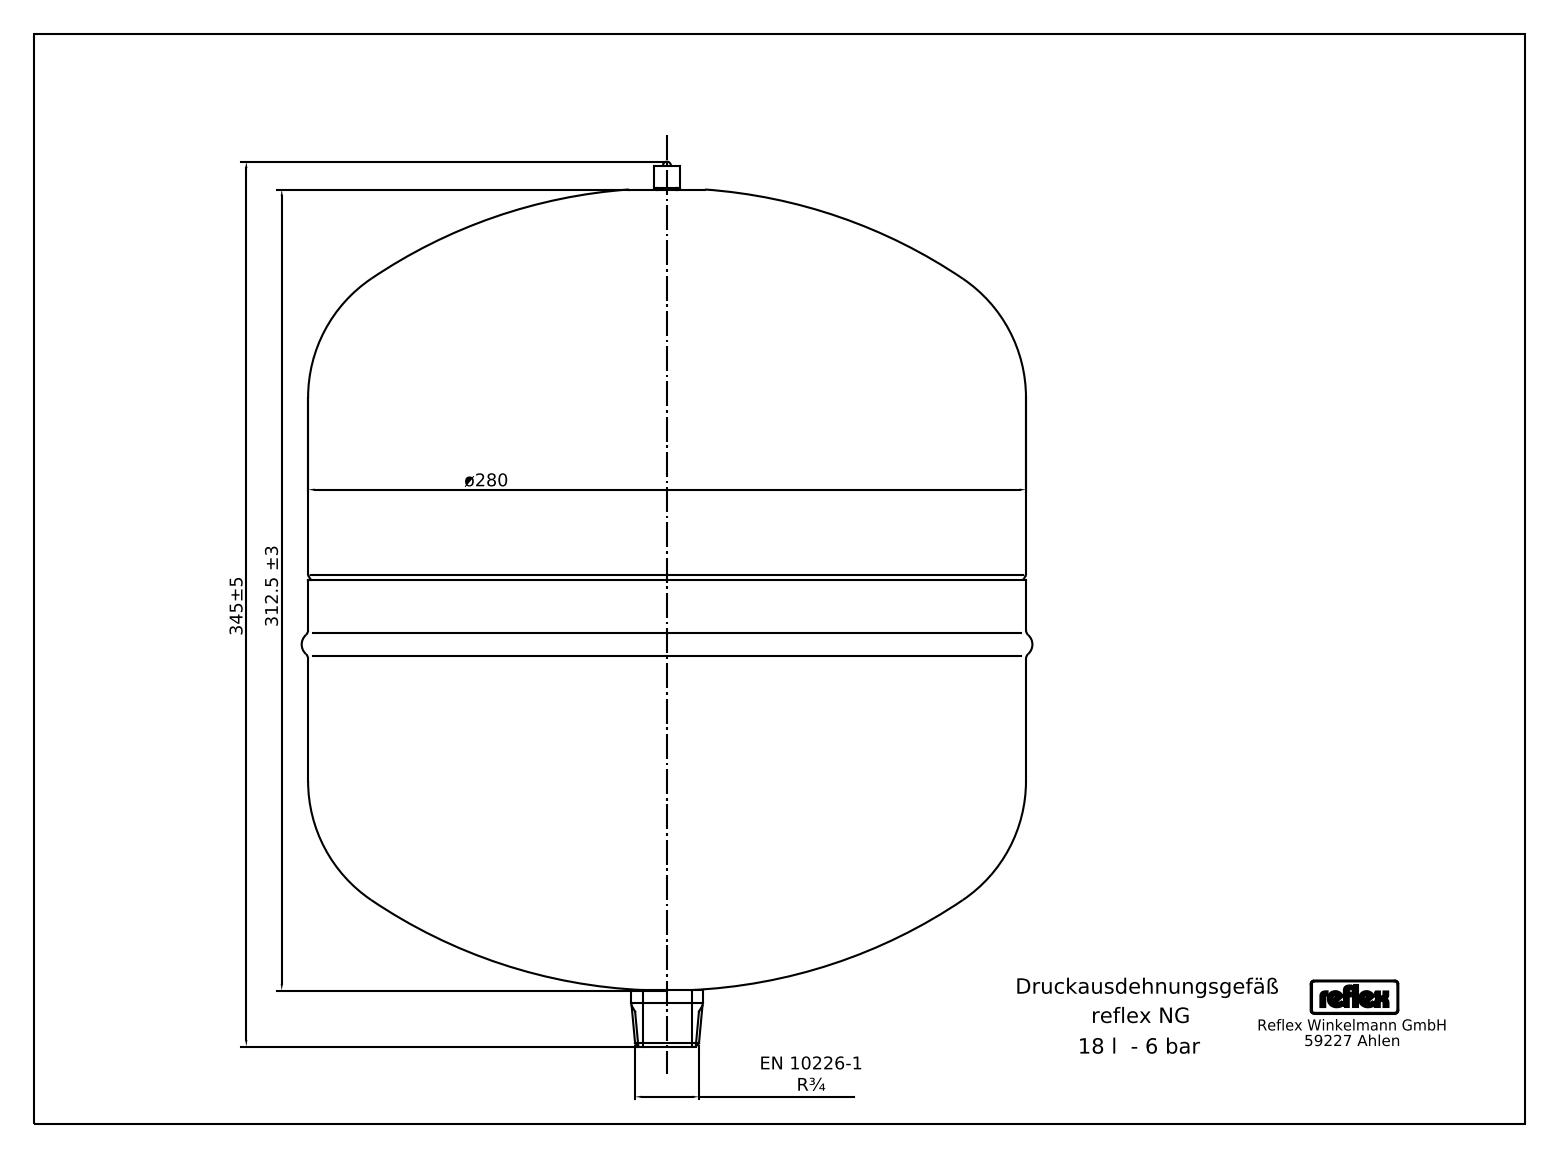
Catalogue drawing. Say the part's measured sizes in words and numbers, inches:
Its 3-D file was written by "Mechanical Desktop 2011 (CONFIG_CONTROL_DESIGN)". It is 13 solids with 125 faces: 64 planar, 38 cylindrical and 23 other. Overall it measures 13.583 by 11.89 by 11.89 inches. Its volume is 1 043 cubic inches and its surface area 976 square inches. Round holes: 1 of diameter 0.744. Round bosses or shafts: 1 of diameter 11.89, 1 of diameter 11.024, 1 of diameter 1.059, 1 of diameter 0.394, 1 of diameter 0.236. Partial cylindrical surfaces (rounded edges, fillets, slot ends): 4 of radius 0.044, 3 of radius 0.018, 2 of radius 0.03, 2 of radius 0.053, 2 of radius 0.073, 2 of radius 0.074, 2 of radius 0.1, 1 of radius 0.022. The main face-to-face distances are 8.031, 3.701, 4.331, 0.63, 0.787, 2.913, 6.614, 7.244, 10.945, 2.126.
